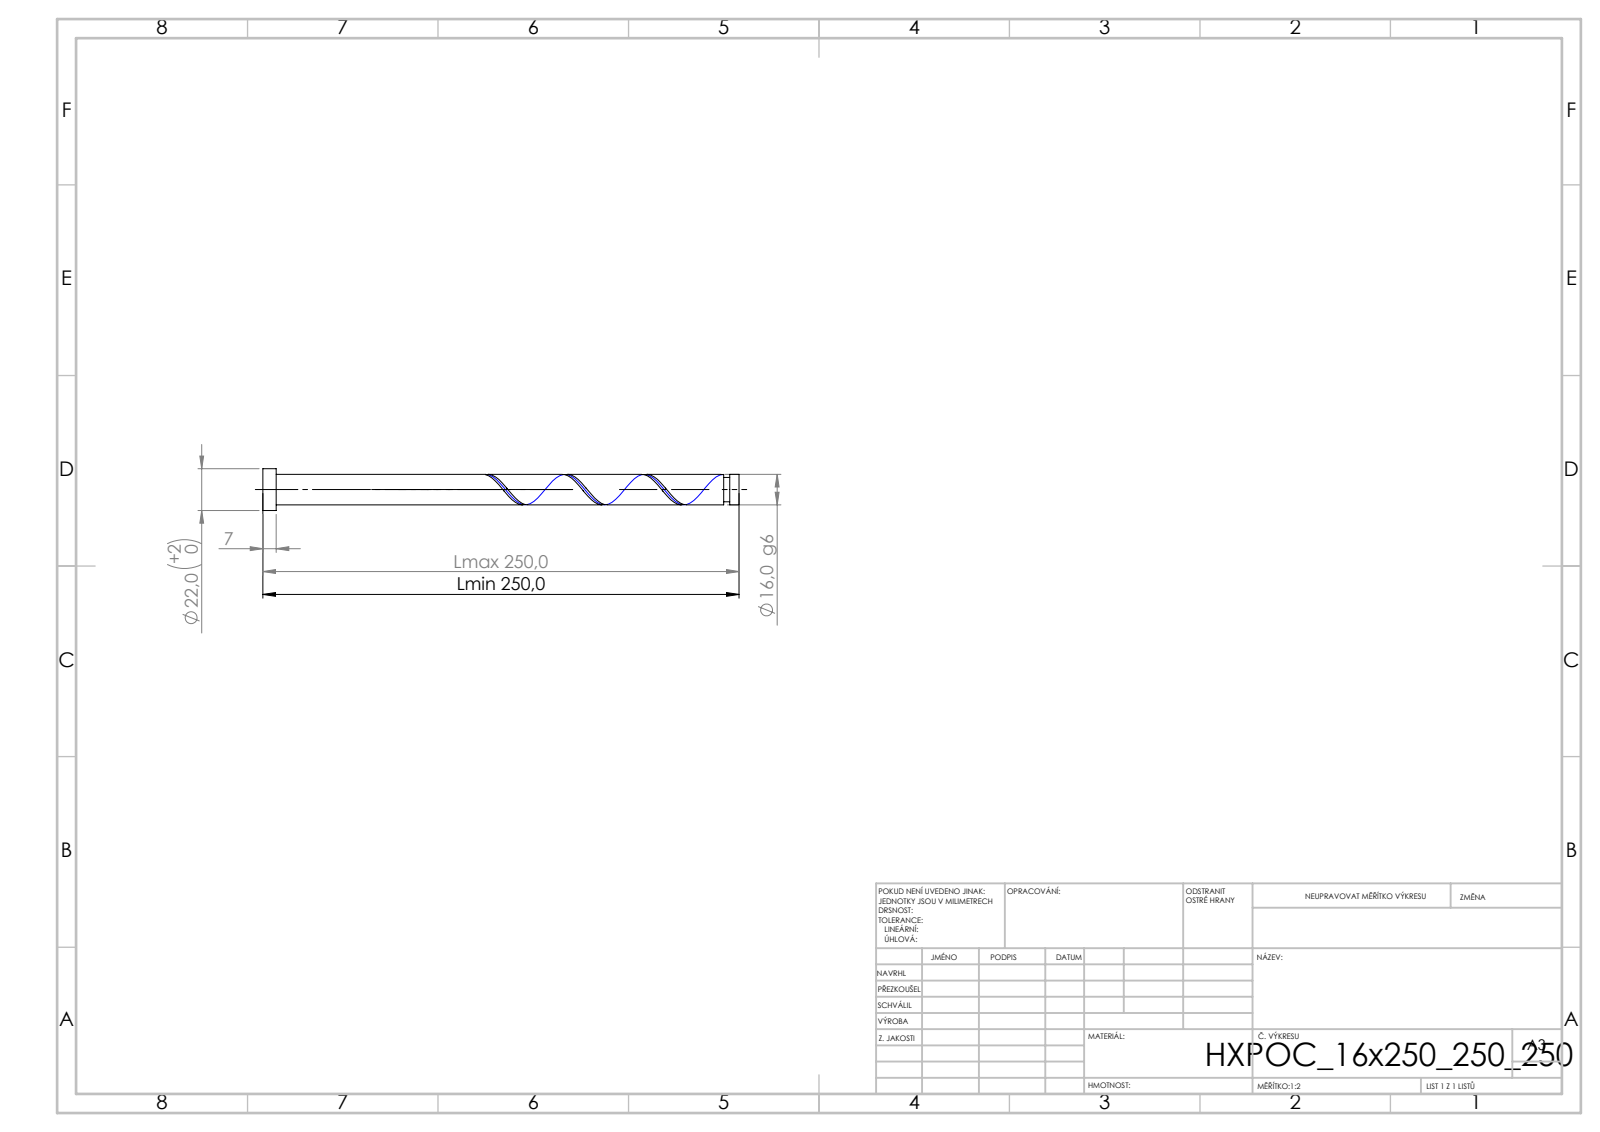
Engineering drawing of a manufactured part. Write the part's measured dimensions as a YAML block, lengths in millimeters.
step_written_by: "SolidWorks 2019 (CONFIG_CONTROL_DESIGN)"
units: millimeters
bodies: {solids: 1, faces: 21, planar: 6, cylindrical: 14, other: 1}
overall_size: [250, 22, 22]
volume: 50806
surface_area: 13924
round_bosses_or_shafts:
  - {diameter: 22, count: 1}
  - {diameter: 16, count: 1}
  - {diameter: 12.8, count: 1}
face_to_face_distances: [250, 7, 243, 245.12, 238.12, 4.88, 241.92, 234.92, 3.2, 8.08]
